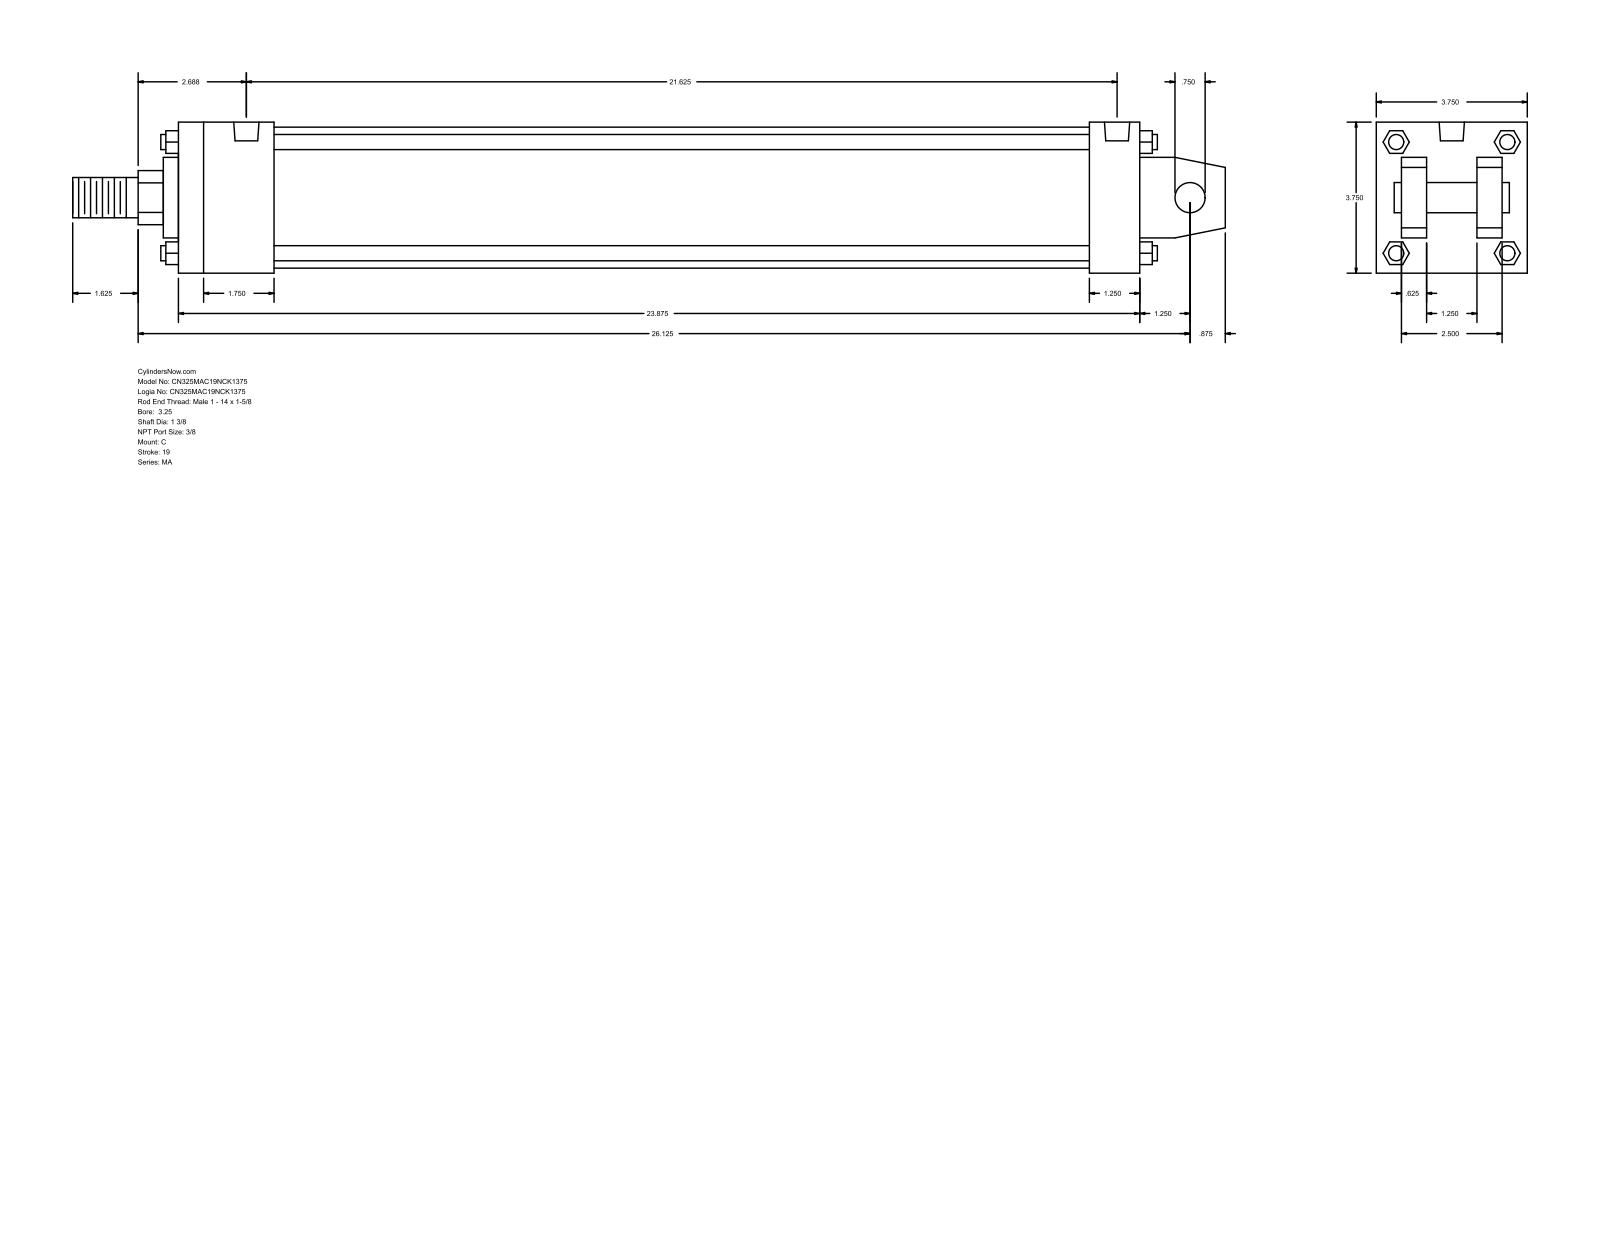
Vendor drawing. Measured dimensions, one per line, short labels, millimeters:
name: MA_C__0325_1.375
written by: GSSL Pune (CONFIG_CONTROL_DESIGN)
unit: mm
bodies: 0 solids, 139 faces (108 planar, 31 cylindrical, 0 other)
size: 727.08 × 95.25 × 95.25
holes: 4× ⌀11.11, 2× ⌀15.93
bosses: 4× ⌀9.53, 1× ⌀88.9, 1× ⌀50.8, 1× ⌀34.92, 1× ⌀25.4, 1× ⌀19.05
rounds: 1× R17.06
face distances: 95.24, 15.87, 63.5, 606.43, 31.74, 79.37, 47.63, 574.68, 31.75, 60.32
hole spacings: 4.77, 539.74, 544.51, 549.28
